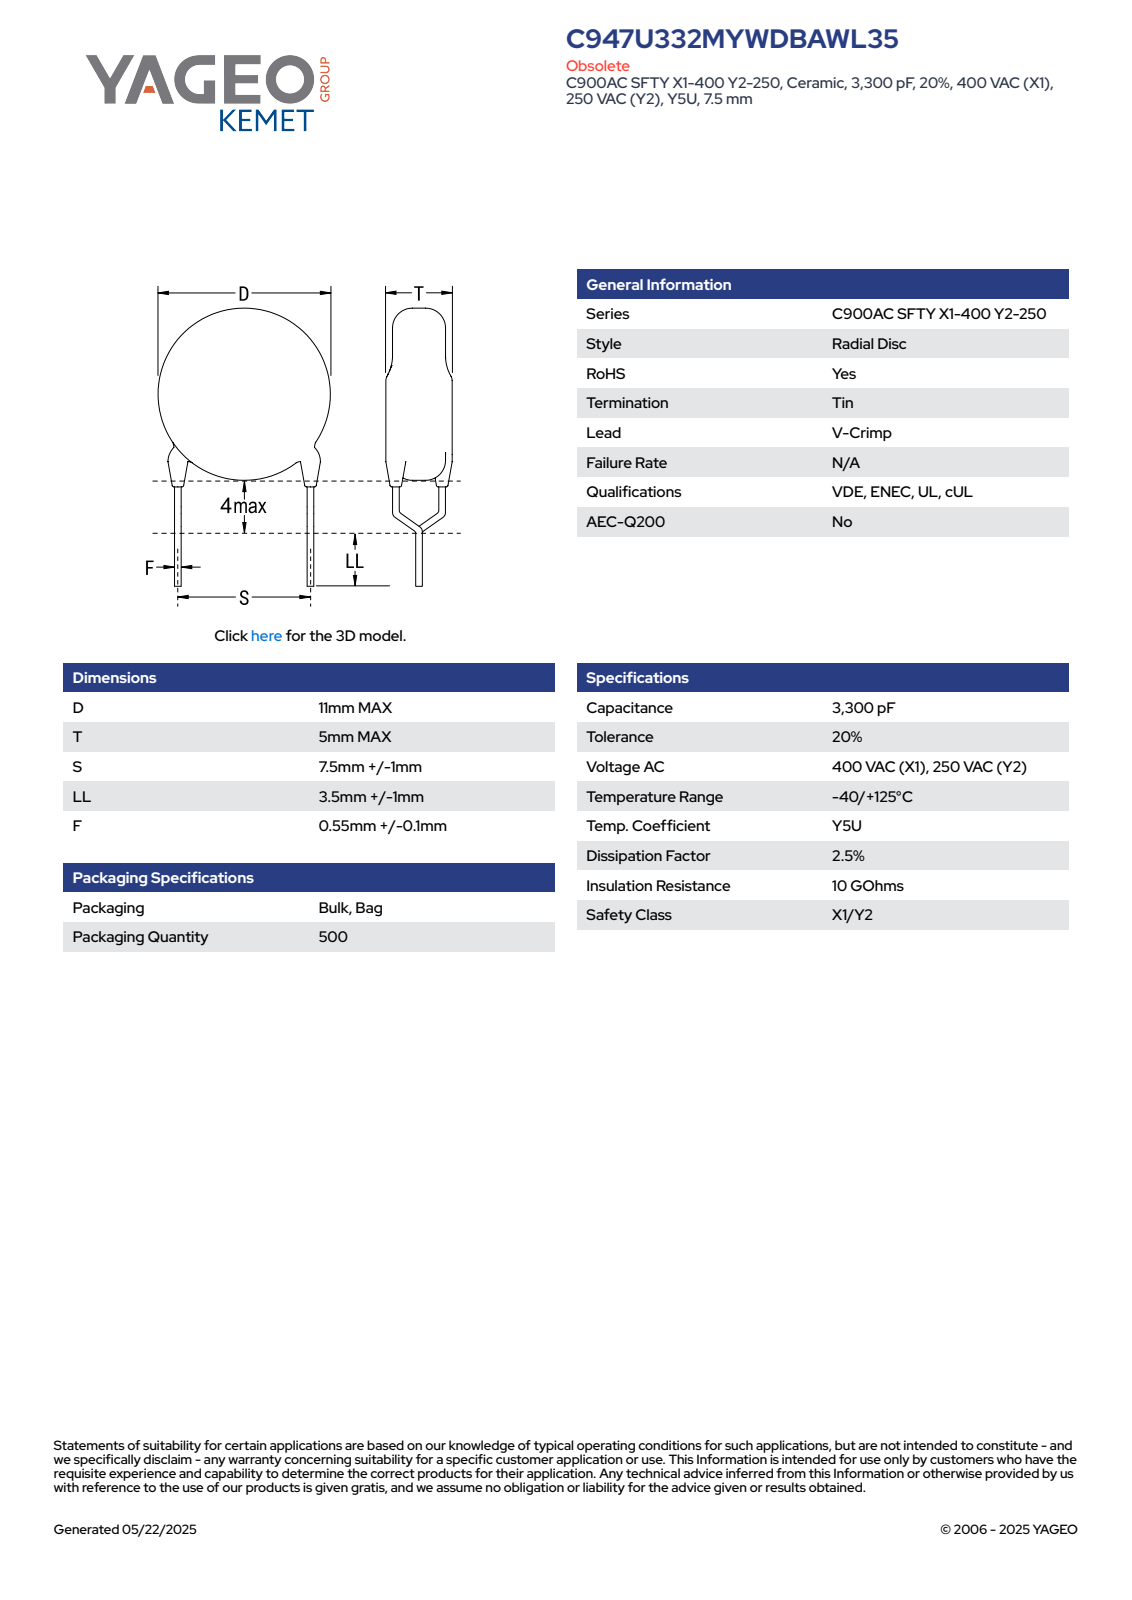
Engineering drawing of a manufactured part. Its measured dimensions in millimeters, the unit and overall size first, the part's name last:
Units: millimetres
Overall size (bounding box): 19.3 × 11 × 5
Round bosses / shafts (diameter × count): ⌀0.65 ×6, ⌀11 ×1
Main face-to-face distances: 5, 7.4, 14.51, 7.11, 13.08, 5.68, 1.43, 0.39, 0.35, 5.84
Volume: 469 mm³ · Surface area: 388 mm²
Bodies: 5 solids, 93 faces (65 planar, 16 cylindrical, 12 other)
Part name (STEP PRODUCT): CCD_VCC900_D11T5S7.5LL4.5F0.65
STEP written by: SolidWorks 2014 (AUTOMOTIVE_DESIGN)
